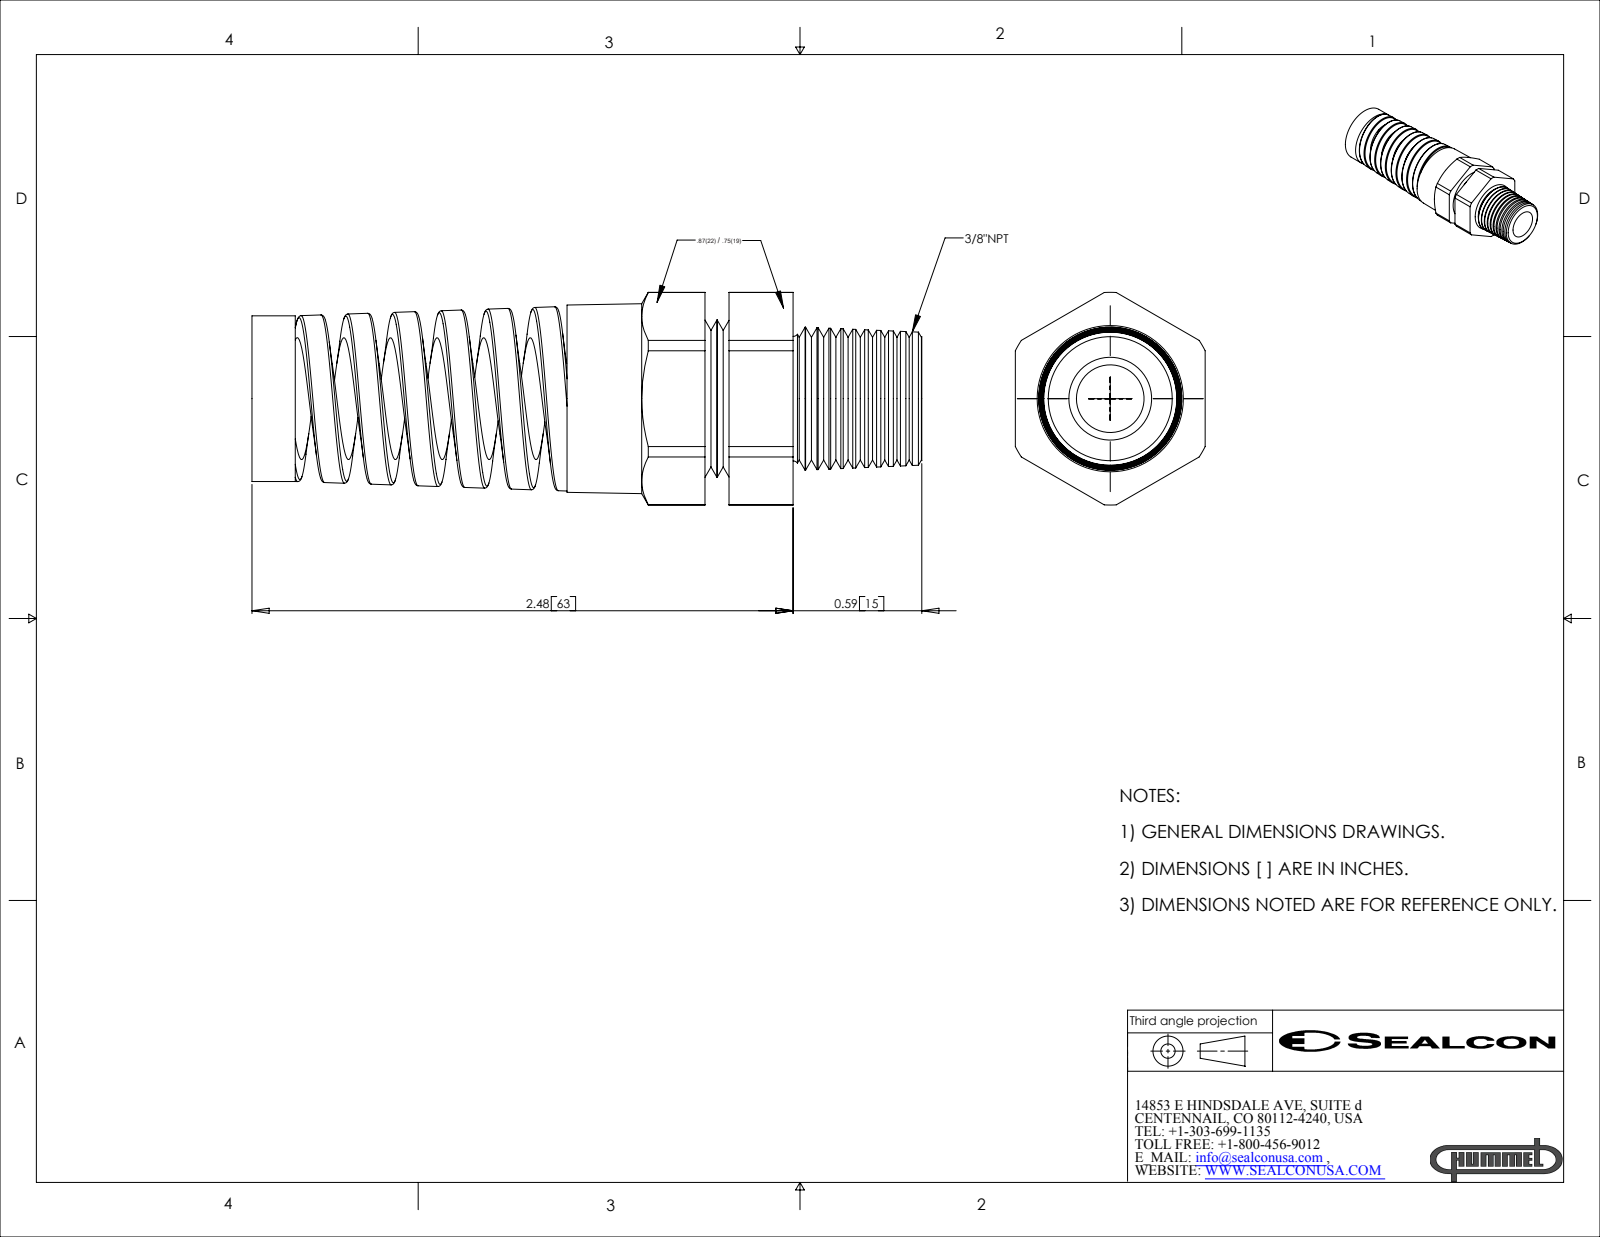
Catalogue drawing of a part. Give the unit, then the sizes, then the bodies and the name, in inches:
Units: inches
Overall size (bounding box): 3.07 × 0.974 × 0.87
Round holes (diameter × count): ⌀0.31 ×1, ⌀0.559 ×1, ⌀0.721 ×1
Round bosses / shafts (diameter × count): ⌀0.759 ×1
Partial cylindrical surfaces — rounded edges, fillets, slot ends (radius × count): R0.487 ×1
Main face-to-face distances: 0.87, 1.036, 0.632, 0.404, 0.742, 0.11, 0.294, 1.444, 2.076, 2.186
Volume: 0.868 in³ · Surface area: 15.19 in²
Bodies: 1 solid, 158 faces (19 planar, 34 cylindrical, 105 other)
Part name (STEP PRODUCT): CF09NA-BK
STEP written by: SolidWorks 2007 (CONFIG_CONTROL_DESIGN)
